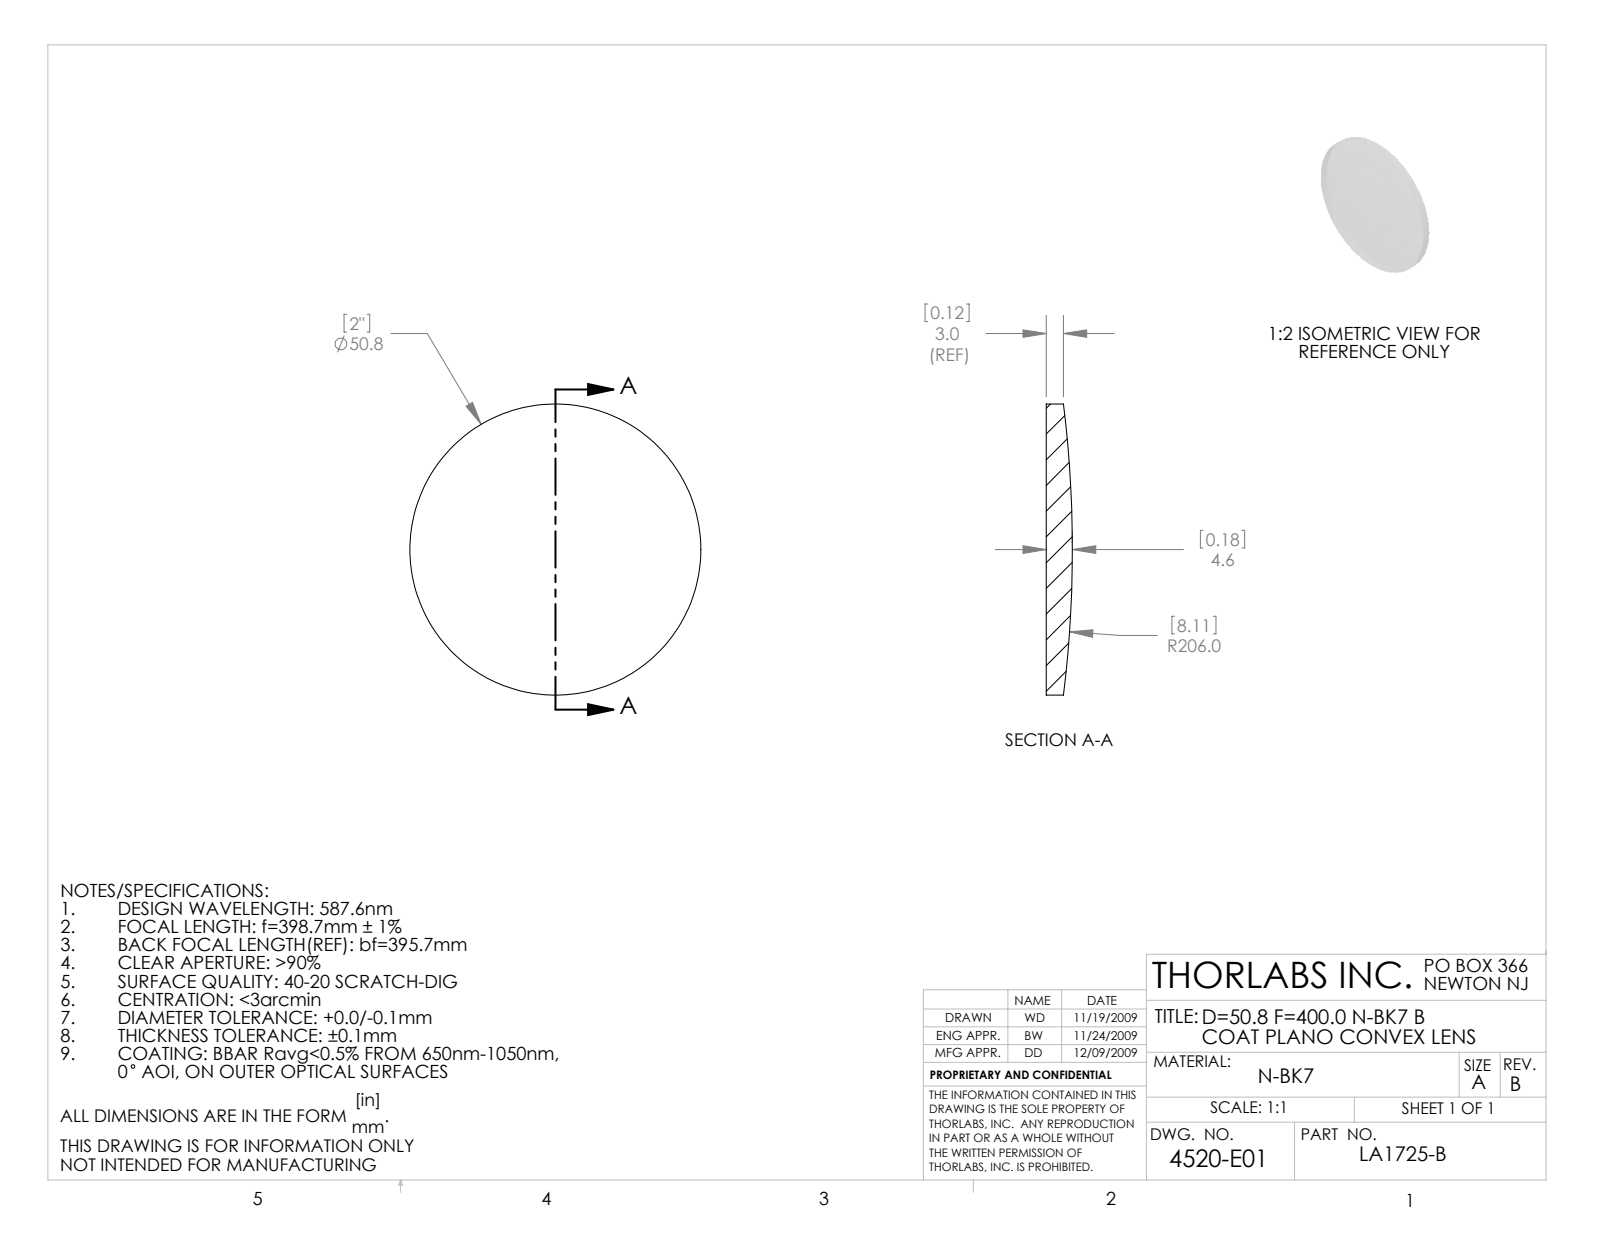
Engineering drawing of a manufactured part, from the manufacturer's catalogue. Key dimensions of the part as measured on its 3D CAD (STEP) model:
Part name (STEP PRODUCT): 4520-E0W
STEP written by: SolidWorks 2009 (AUTOMOTIVE_DESIGN)
Units: millimetres
Bodies: 1 solid, 5 faces (1 planar, 2 cylindrical, 2 other)
Overall size (bounding box): 50.8 × 50.8 × 4.57
Volume: 7 672 mm³ · Surface area: 4 540 mm²
Round bosses / shafts (diameter × count): ⌀50.8 ×1
